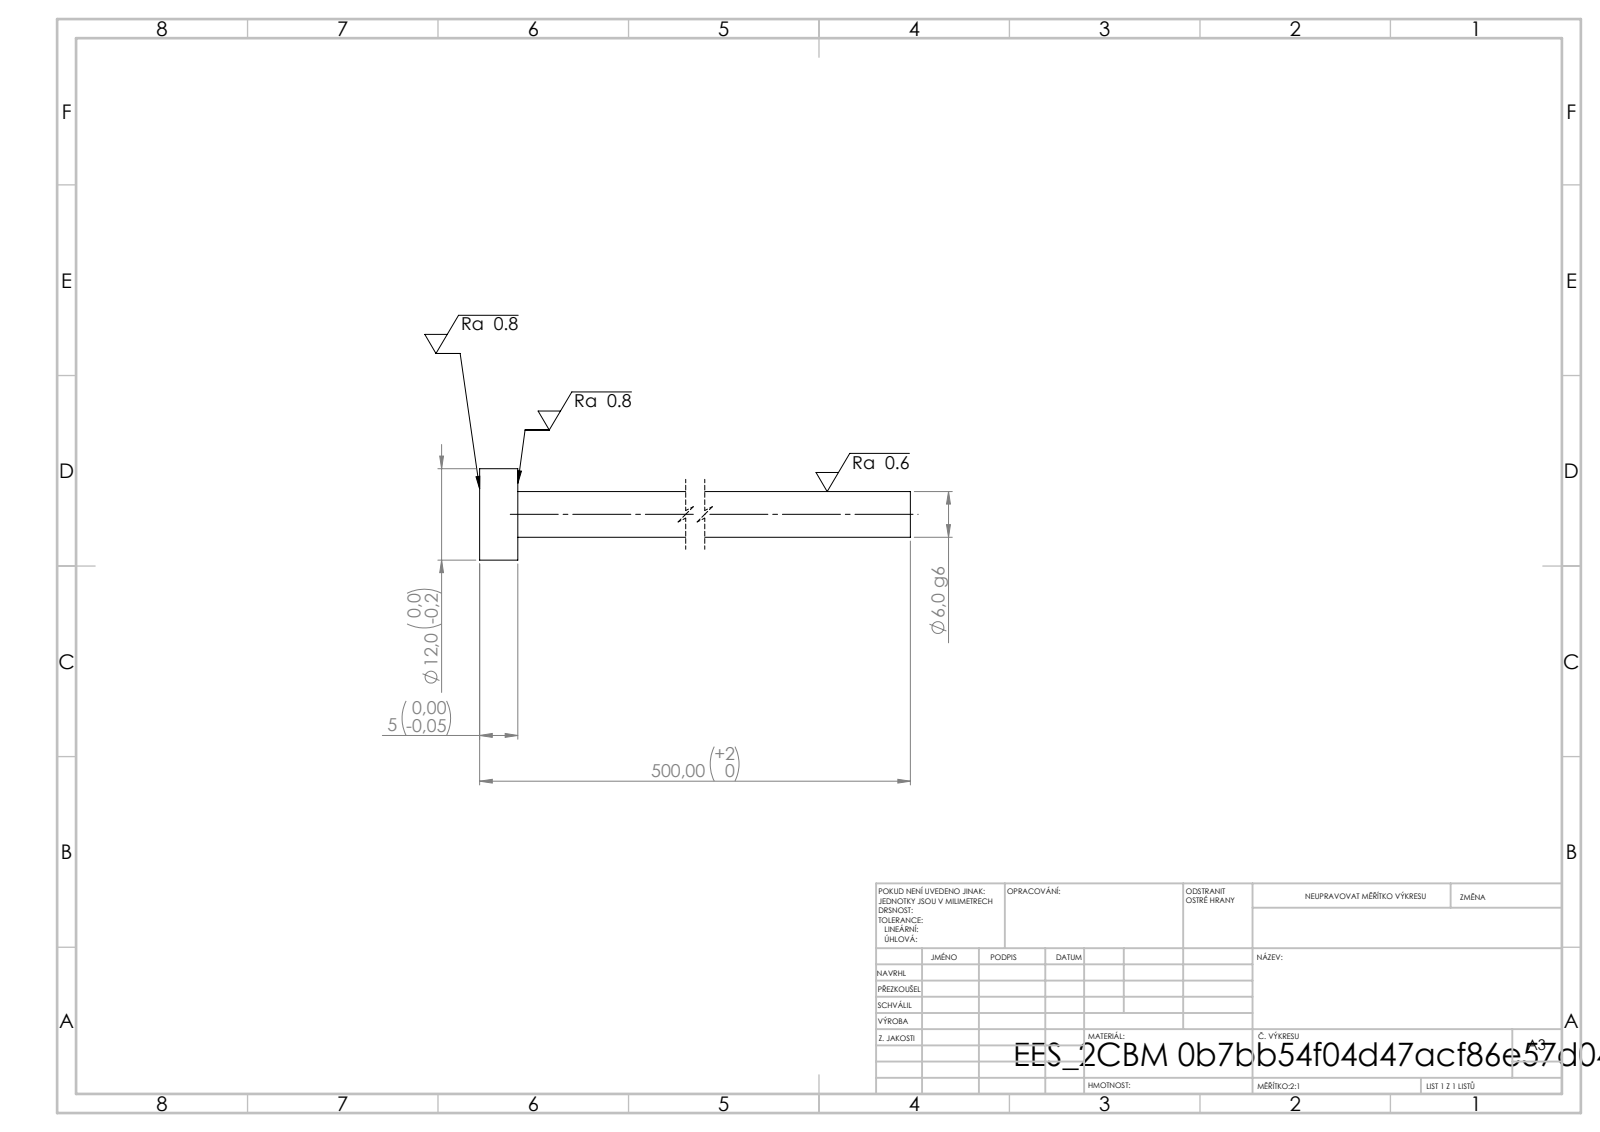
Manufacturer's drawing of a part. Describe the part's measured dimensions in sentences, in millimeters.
Its 3-D file was written by "SolidWorks 2019 (CONFIG_CONTROL_DESIGN)". It is 1 solid with 7 faces: 3 planar, 4 cylindrical and 0 other. Overall it measures 500 by 12 by 12 millimeters. Its volume is 14 561 cubic millimeters and its surface area 9 745 square millimeters. Round bosses or shafts: 1 of diameter 12, 1 of diameter 6. The main face-to-face distances are 5, 500, 495.
